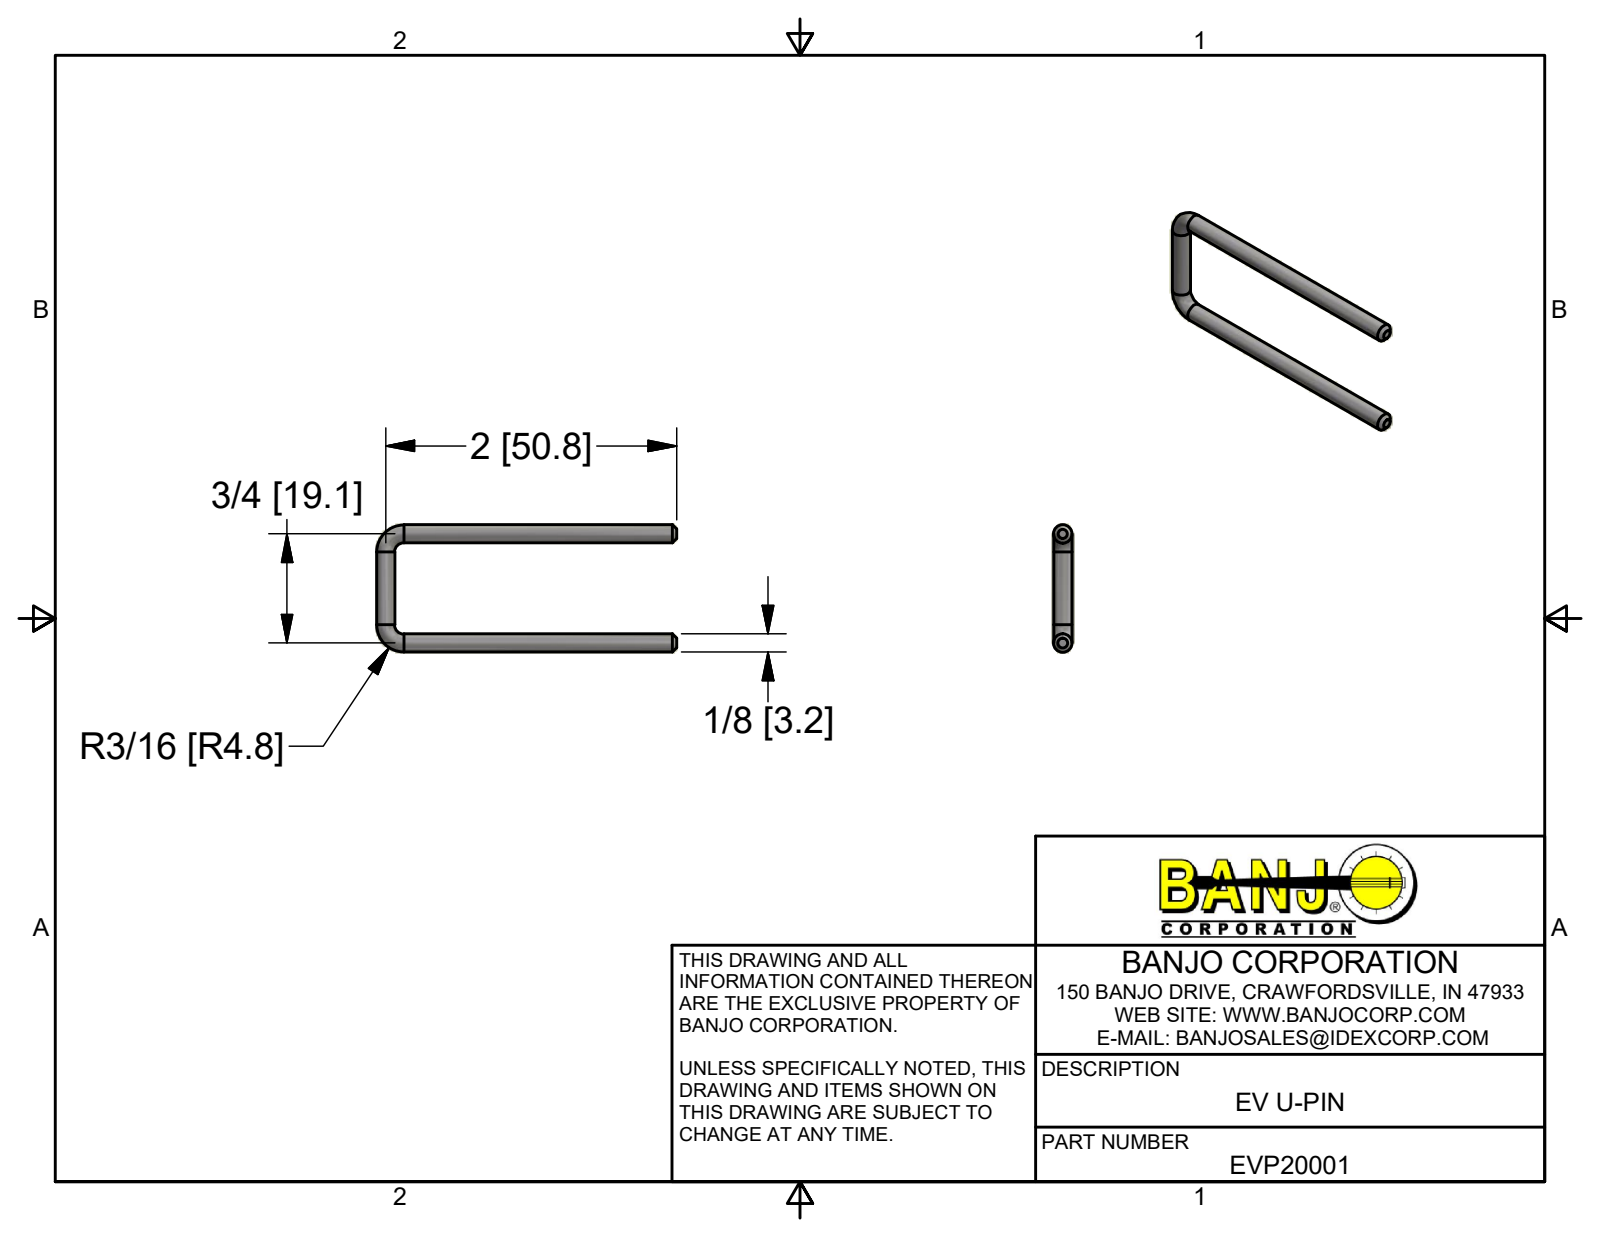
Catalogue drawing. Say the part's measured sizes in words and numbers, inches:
The part is named "EVP20001". Its 3-D file was written by "Autodesk Inventor 2018 (AUTOMOTIVE_DESIGN)". It is 1 solid with 9 faces: 2 planar, 3 cylindrical and 4 other. Overall it measures 2.062 by 0.875 by 0.125 inches. Its volume is 0.057 cubic inches and its surface area 1.832 square inches. Round bosses or shafts: 3 of diameter 0.125.
